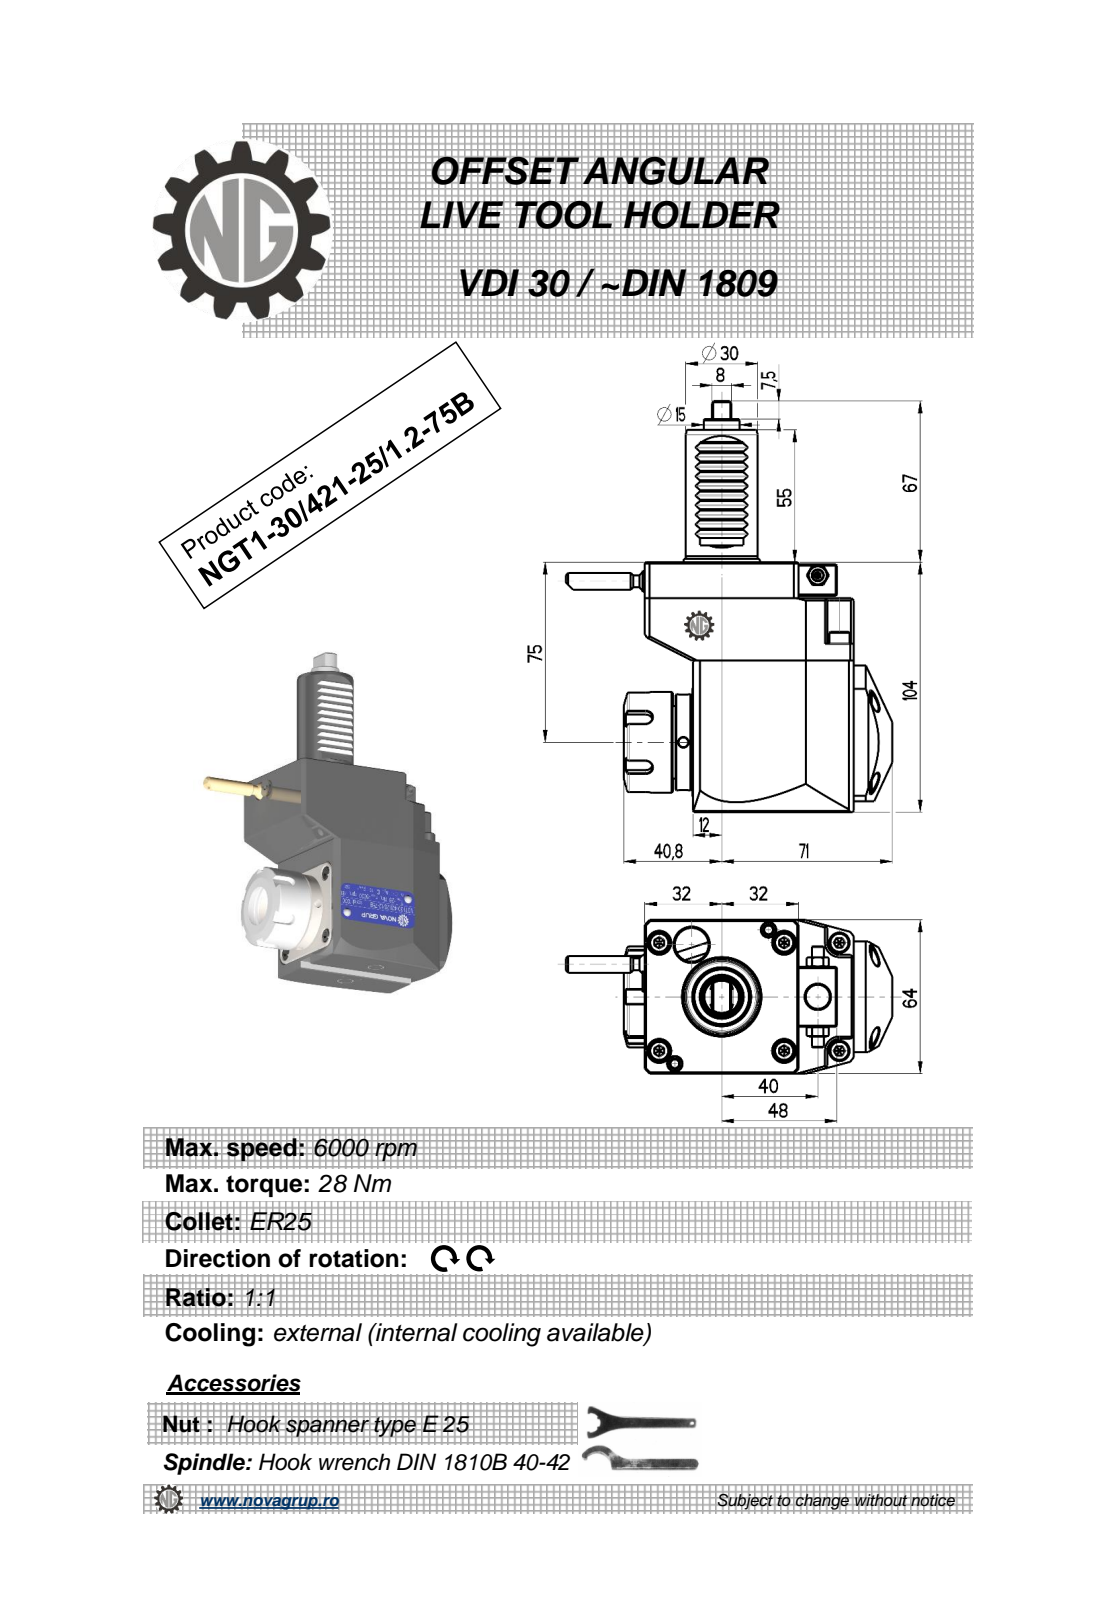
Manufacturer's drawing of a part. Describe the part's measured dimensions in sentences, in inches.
The part is named "NGT1_30_421_25_1_2_75B". Its 3-D file was written by "PRO/ENGINEER BY PARAMETRIC TECHNOLOGY CORPORATION, 2010280 (CONFIG_CONTROL_DESIGN)". It is 1 solid with 462 faces: 222 planar, 94 cylindrical and 146 other. Overall it measures 6.732 by 5.35 by 2.575 inches. Its volume is 34.22 cubic inches and its surface area 83.59 square inches. Round holes: 2 of diameter 0.157, 1 of diameter 0.098, 1 of diameter 0.118, 1 of diameter 0.165, 1 of diameter 0.374, 1 of diameter 0.394, 1 of diameter 0.799. Round bosses or shafts: 2 of diameter 0.353, 2 of diameter 0.197, 1 of diameter 1.654, 1 of diameter 1.575, 1 of diameter 1.299, 1 of diameter 1.181, 1 of diameter 0.591, 1 of diameter 0.276. Partial cylindrical surfaces (rounded edges, fillets, slot ends): 12 of radius 0.01, 10 of radius 0.012, 5 of radius 0.118, 4 of radius 0.138, 2 of radius 0.031, 2 of radius 0.157, 1 of radius 0.283, 1 of radius 1.26. The main face-to-face distances are 2.52, 4.094, 3.425, 2.646, 0.78, 0.787, 0.591, 2.638, 3.504, 2.165. The hole center spacings are 0.533, 2.203, 2.677, 2.691, 3.513.
